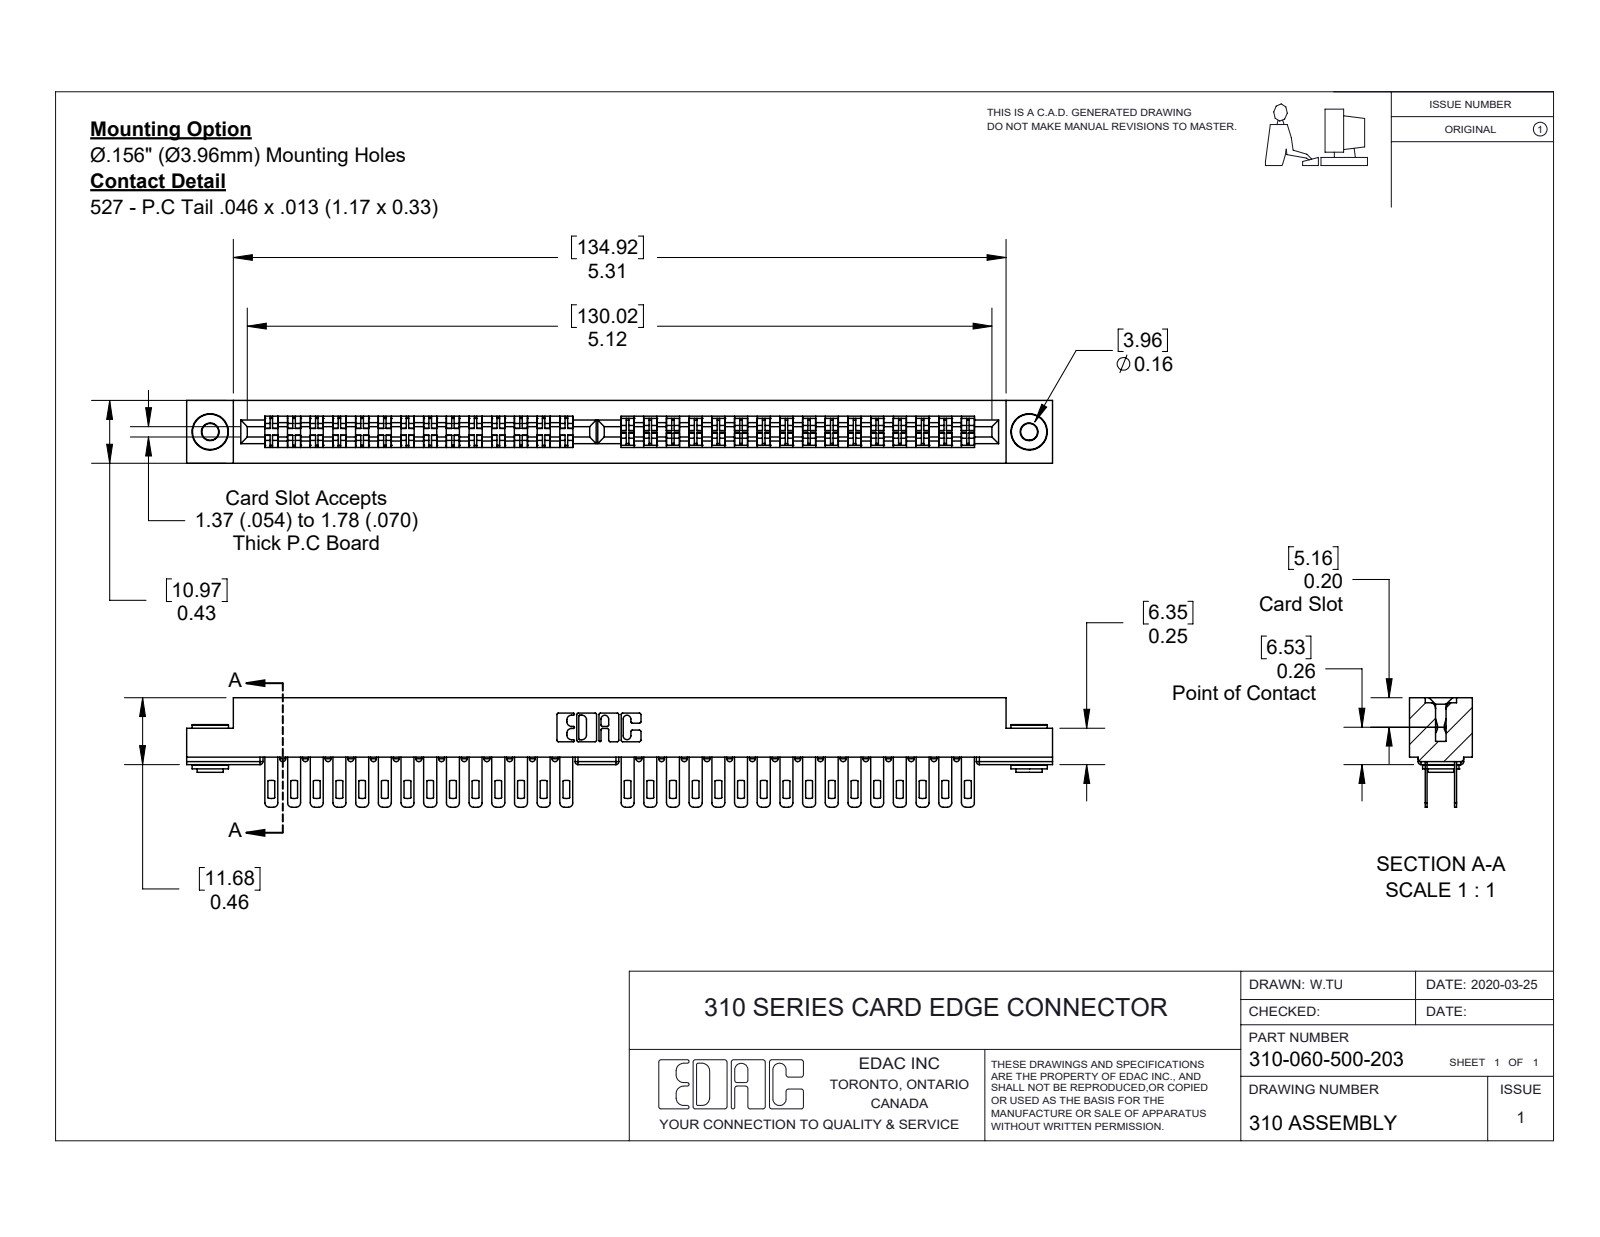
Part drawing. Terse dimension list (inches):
name: 345-250-002_345-250-002-102; 310-060-500-203; 310 Part_.116 Hex; 307-290-001_500
written by: SolidWorks 2016 (CONFIG_CONTROL_DESIGN)
unit: in
bodies: 63 solids, 2978 faces (1908 planar, 998 cylindrical, 72 other)
size: 5.953 × 0.753 × 0.432
volume: 0.805 in³; area: 29.75 in²
holes: 2× ⌀0.116, 2× ⌀0.156
bosses: 2× ⌀0.25, 2× ⌀0.18, 2× ⌀0.136
rounds: 98× R0.02, 60× R0.03, 30× R0.063, 22× R0.01, 6× R0.007, 6× R0.031, 4× R0.012, 4× R0.025
face distances: 0.109, 0.324, 0.013, 0.015, 0.187, 0.432, 0.124, 0.309, 0.2, 0.215
hole spacings: 5.63
